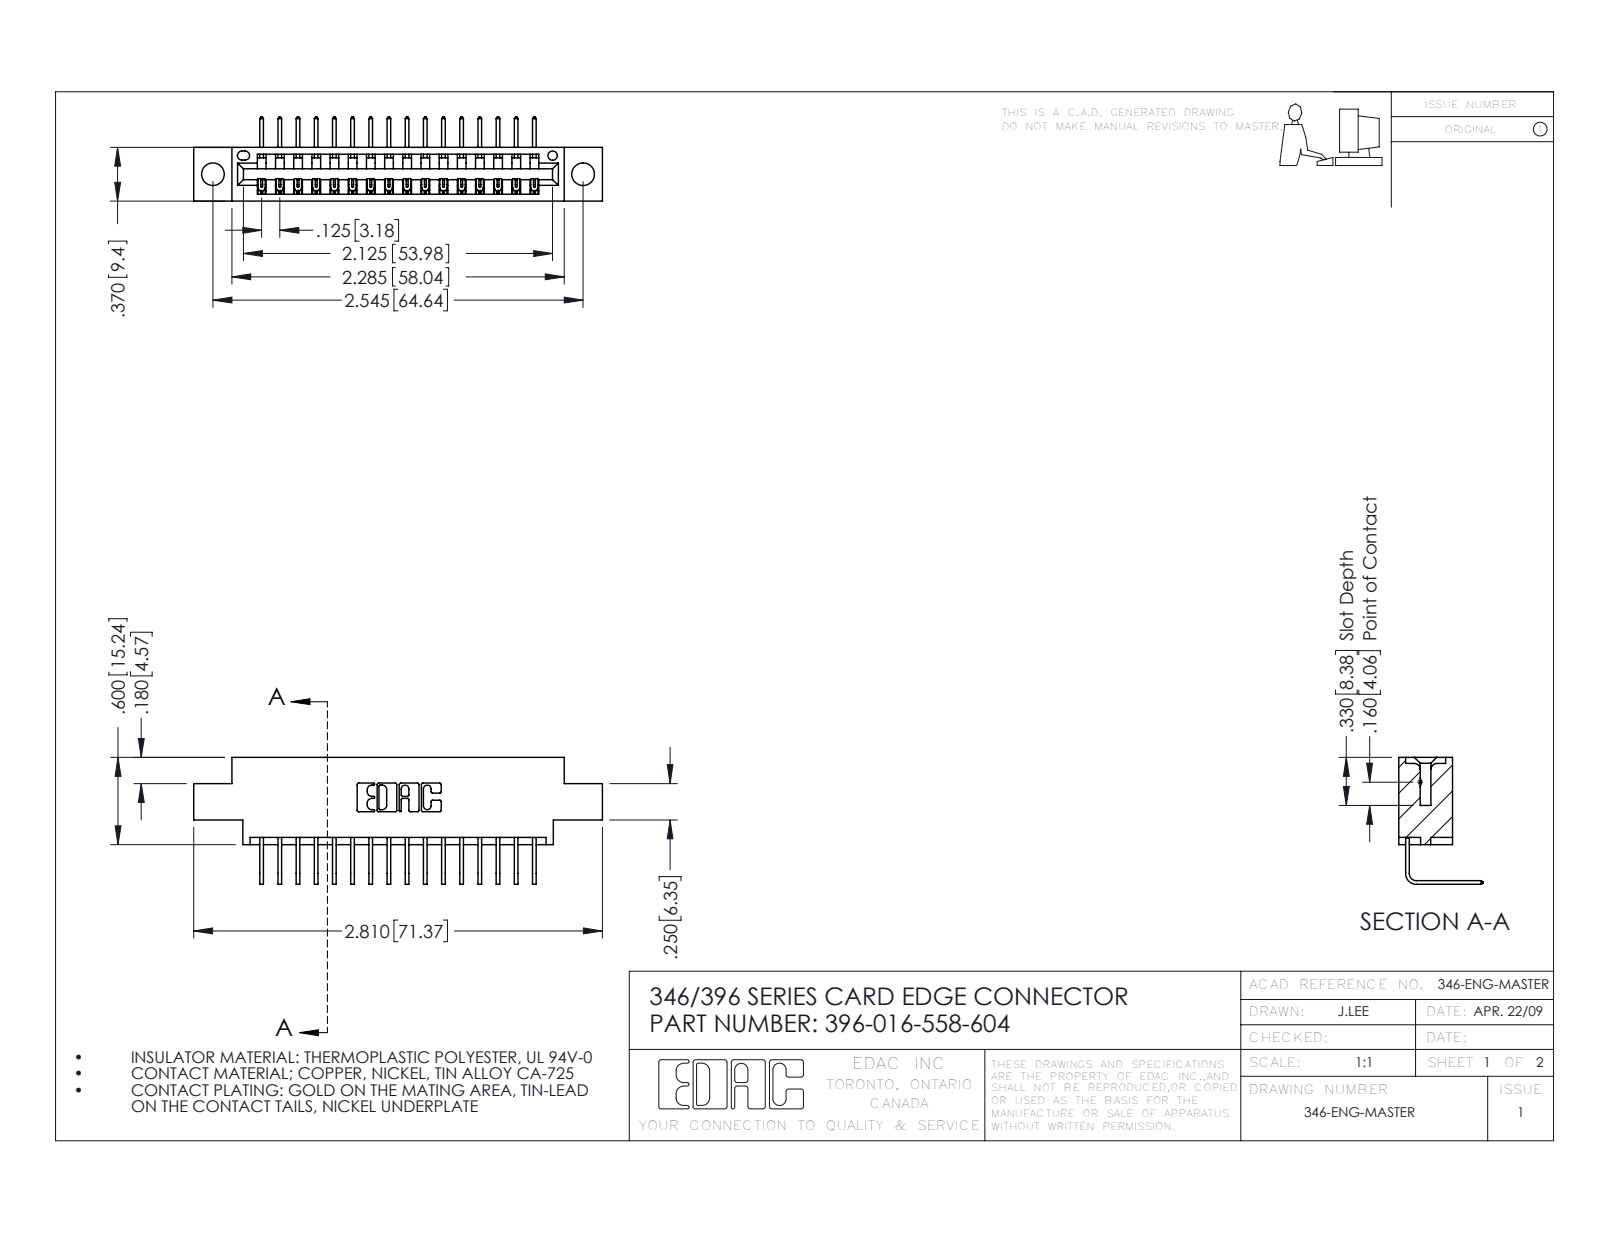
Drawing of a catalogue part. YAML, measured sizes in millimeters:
part_name: "345-292-001_558 Tail - 2; 396-016-558-604; 346 Part_0.170 Offset - 0.156 Dia-TH"
step_written_by: "SolidWorks 2016 (CONFIG_CONTROL_DESIGN)"
units: millimeters
bodies: {solids: 17, faces: 1086, planar: 752, cylindrical: 334, other: 0}
overall_size: [71.4, 22.2, 14.7]
volume: 6460
surface_area: 8084
round_holes:
  - {diameter: 4, count: 2}
  - {diameter: 1.6, count: 1}
partial_cylinders:
  - {radius: 0.2, count: 32}
  - {radius: 0.3, count: 22}
  - {radius: 0.2, count: 6}
  - {radius: 0.8, count: 6}
  - {radius: 0.7, count: 3}
  - {radius: 0.8, count: 2}
  - {radius: 1, count: 2}
  - {radius: 0.4, count: 1}
face_to_face_distances: [8.2, 9.4, 1.2, 6.4, 7.6, 0.6, 1.8, 3.8, 5.6, 2.5]
hole_center_spacings: [6.2, 59.4, 64.6]
